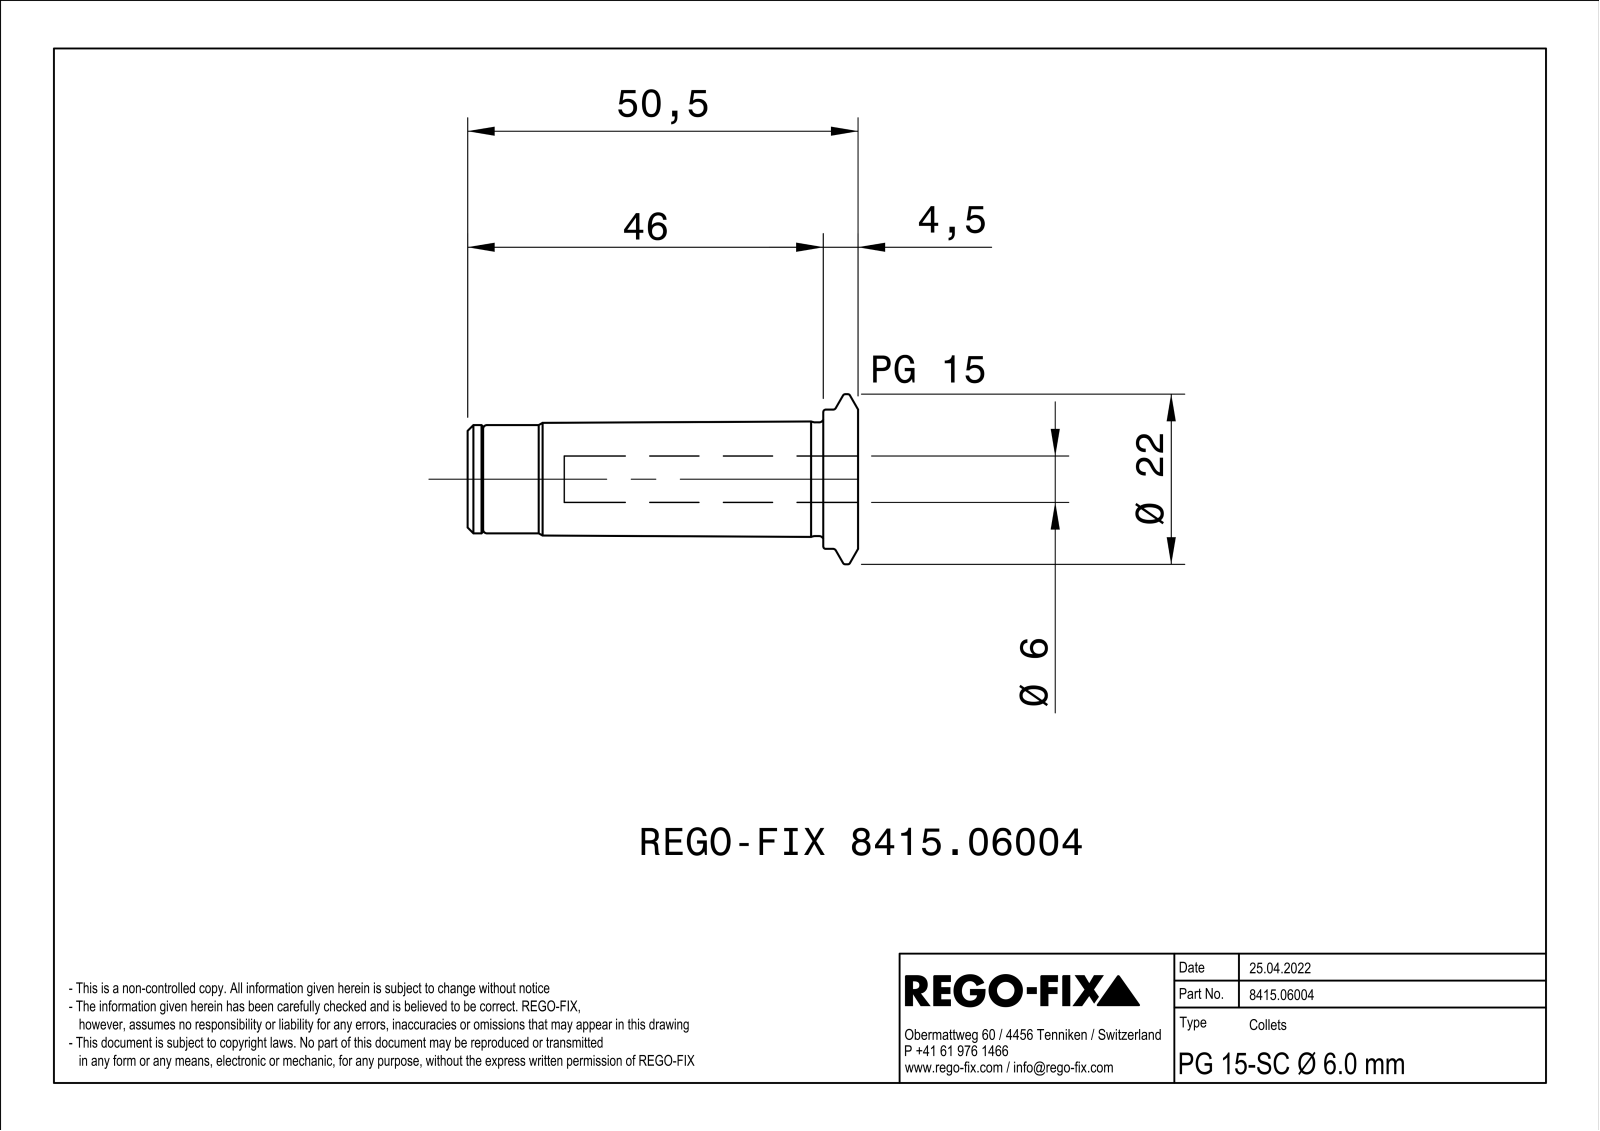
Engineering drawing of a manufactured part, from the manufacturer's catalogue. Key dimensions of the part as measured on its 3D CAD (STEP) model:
Part name (STEP PRODUCT): 0024236
STEP written by: SIEMENS PLM Software Solid Edge ST10 (AUTOMOTIVE_DESIGN)
Units: millimetres
Bodies: 2 solids, 109 faces (39 planar, 31 cylindrical, 39 other)
Overall size (bounding box): 50.5 × 22 × 22
Volume: 7 096 mm³ · Surface area: 5 722 mm²
Round holes (diameter × count): ⌀1.5 ×2, ⌀6 ×1, ⌀6.92 ×1, ⌀7.2 ×1, ⌀8.2 ×1, ⌀8.5 ×1, ⌀10.92 ×1, ⌀12.2 ×1
Round bosses / shafts (diameter × count): ⌀22 ×1, ⌀18 ×1, ⌀14.7 ×1, ⌀14 ×1
Partial cylindrical surfaces — rounded edges, fillets, slot ends (radius × count): R0.15 ×4, R5.2 ×1, R6 ×1
Main face-to-face distances: 48.5, 2, 50.5, 8, 3, 4.65, 4.35, 4.5, 44, 46
